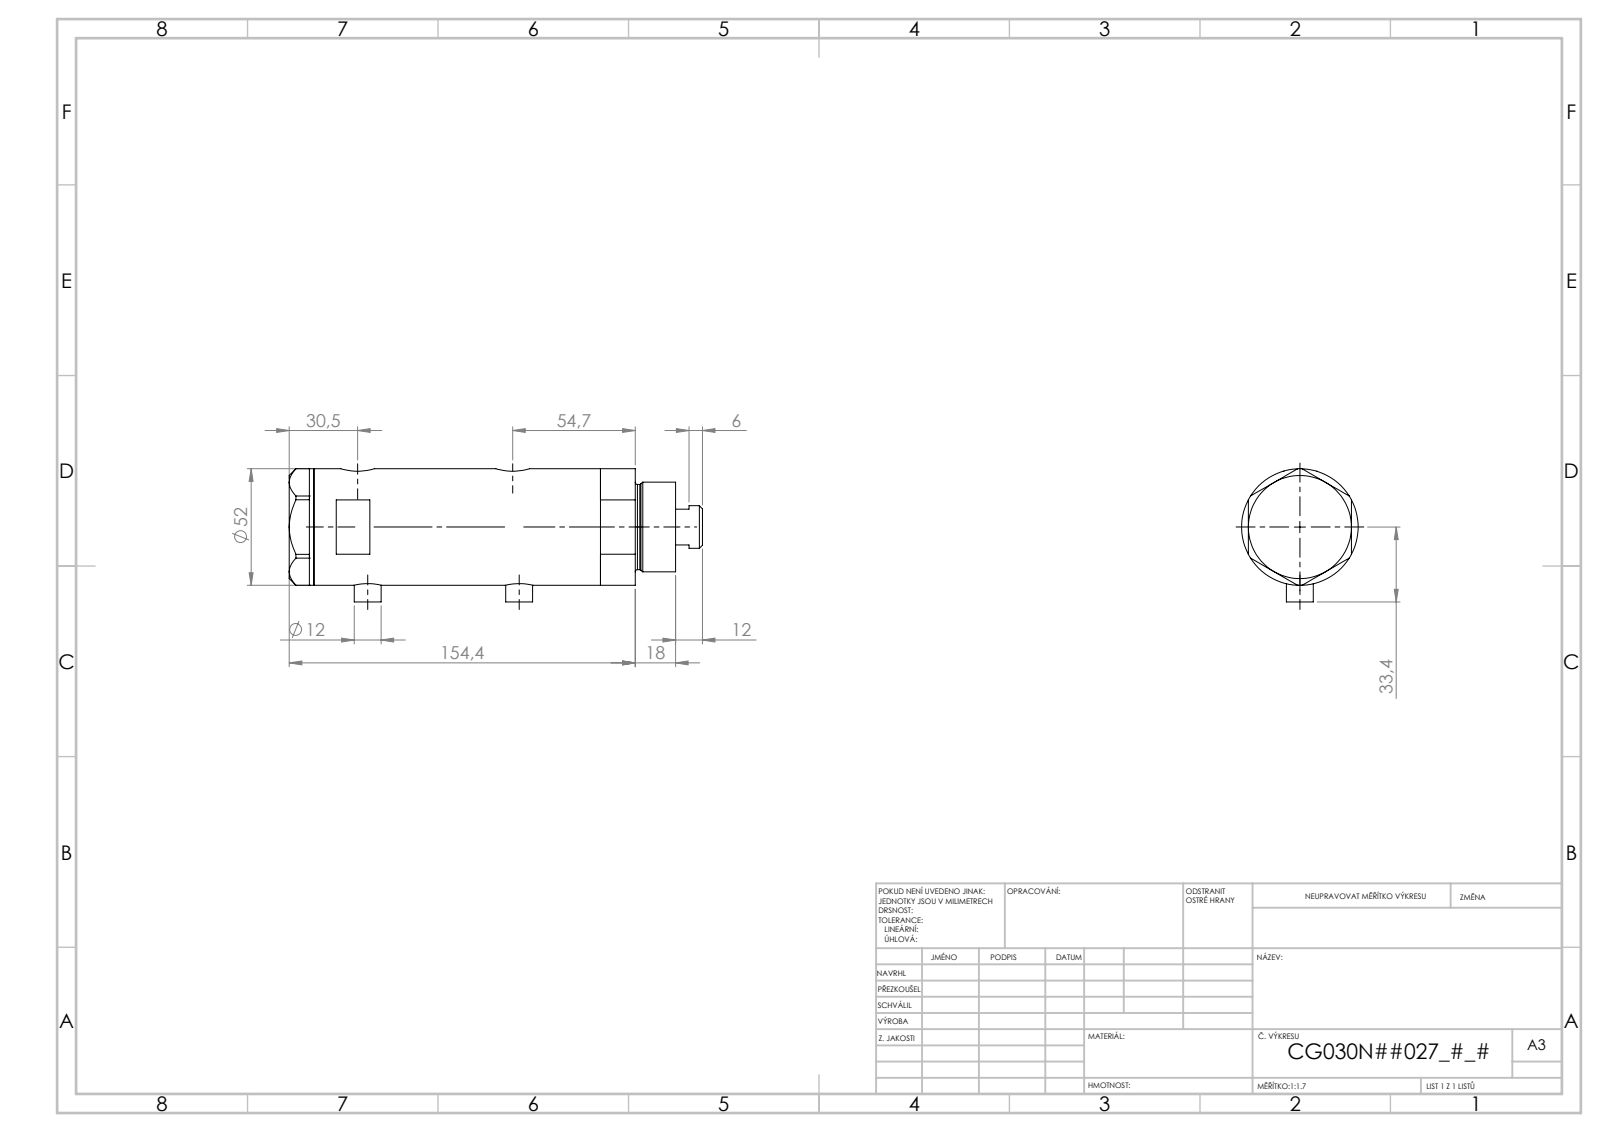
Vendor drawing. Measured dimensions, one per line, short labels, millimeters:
name: V270CG_FRONT; V270CG_VC; V270CG_MIDDLE; V270CG_BACK
written by: SolidWorks 2019 (CONFIG_CONTROL_DESIGN)
unit: mm
bodies: 4 solids, 140 faces (67 planar, 53 cylindrical, 20 other)
size: 176.02 × 53.1 × 52
volume: 314 256 mm³; area: 73 741 mm²
holes: 2× ⌀5, 2× ⌀9.73, 2× ⌀12.5, 2× ⌀15, 1× ⌀6.5, 1× ⌀20, 1× ⌀21.5, 1× ⌀30, 1× ⌀33, 1× ⌀44
bosses: 2× ⌀12, 1× ⌀52, 1× ⌀40, 1× ⌀38, 1× ⌀19
face distances: 23.81, 10.99, 34.8, 46, 91.55, 80.56, 56.75, 127.95, 116.96, 93.15
hole spacings: 2.9, 4.5, 53.75, 56.65, 58.25, 61.15, 2.89, 2.91
